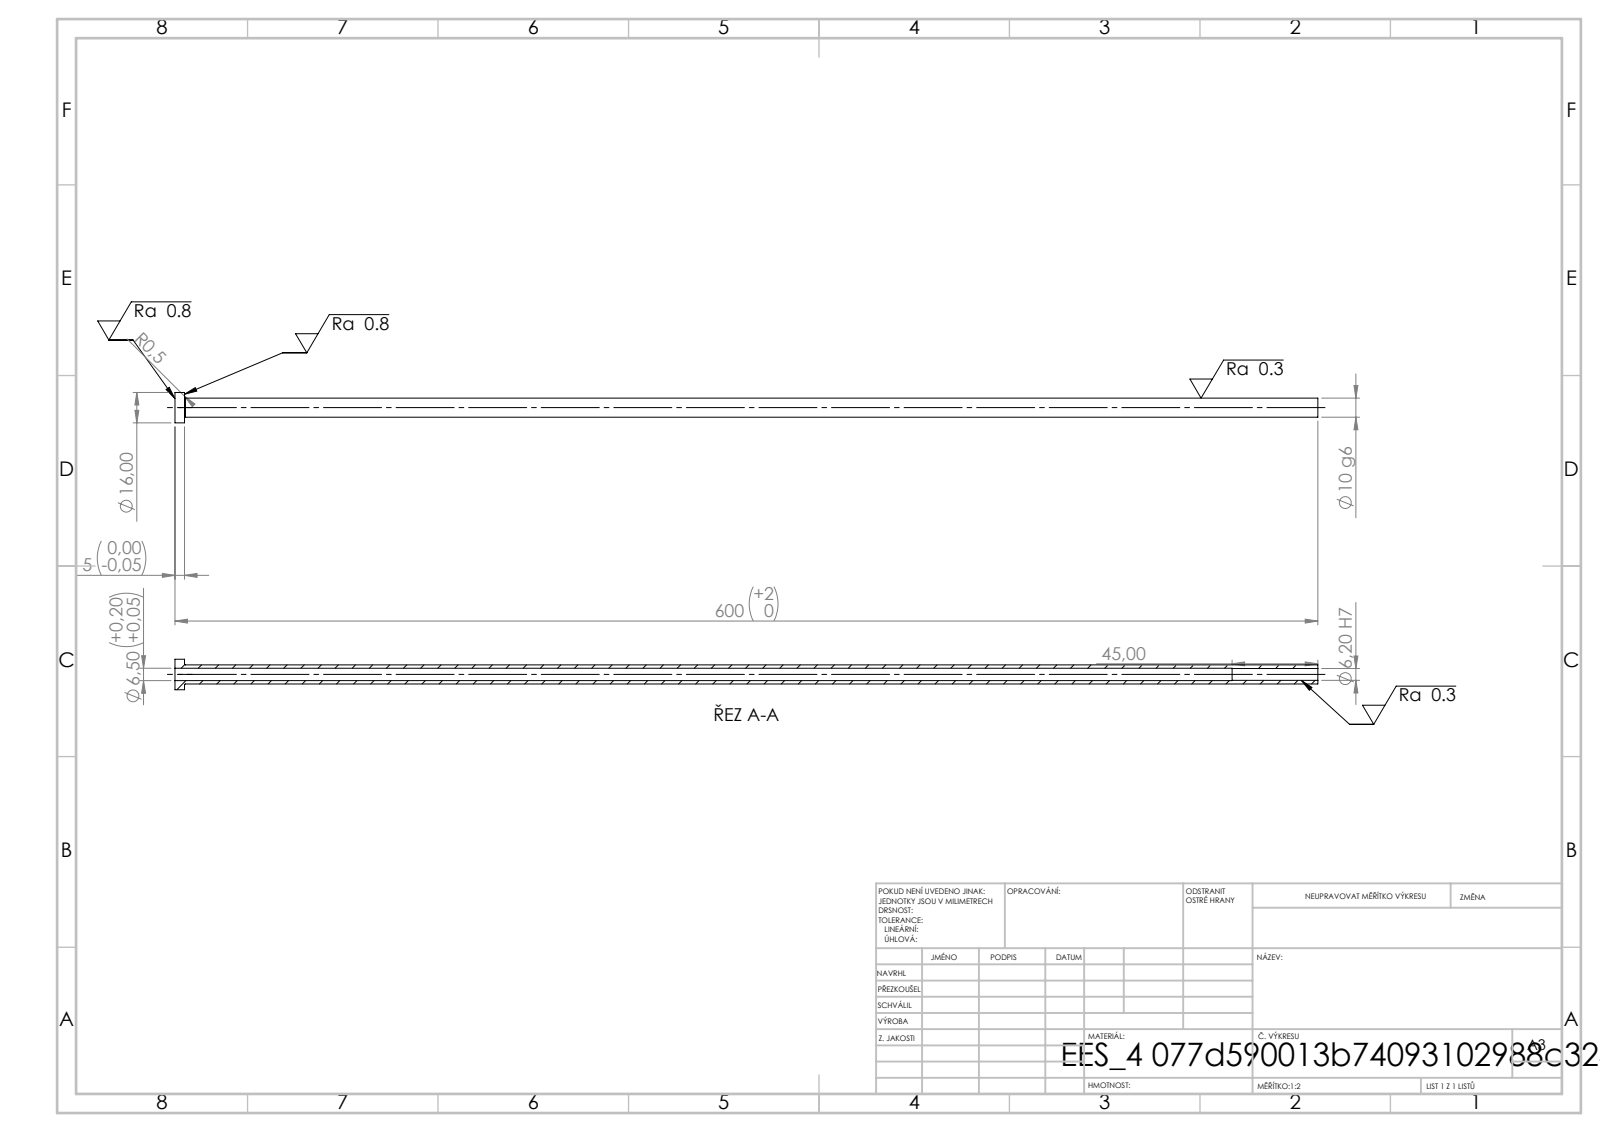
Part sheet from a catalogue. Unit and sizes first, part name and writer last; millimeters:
Units: millimetres
Overall size (bounding box): 600 × 16 × 16
Round holes (diameter × count): ⌀6.2 ×1, ⌀6.5 ×1
Round bosses / shafts (diameter × count): ⌀16 ×1, ⌀10 ×1
Main face-to-face distances: 5, 600, 595, 555, 550, 45
Volume: 27 963 mm³ · Surface area: 31 489 mm²
Bodies: 1 solid, 14 faces (4 planar, 8 cylindrical, 2 other)
STEP written by: SolidWorks 2019 (CONFIG_CONTROL_DESIGN)
